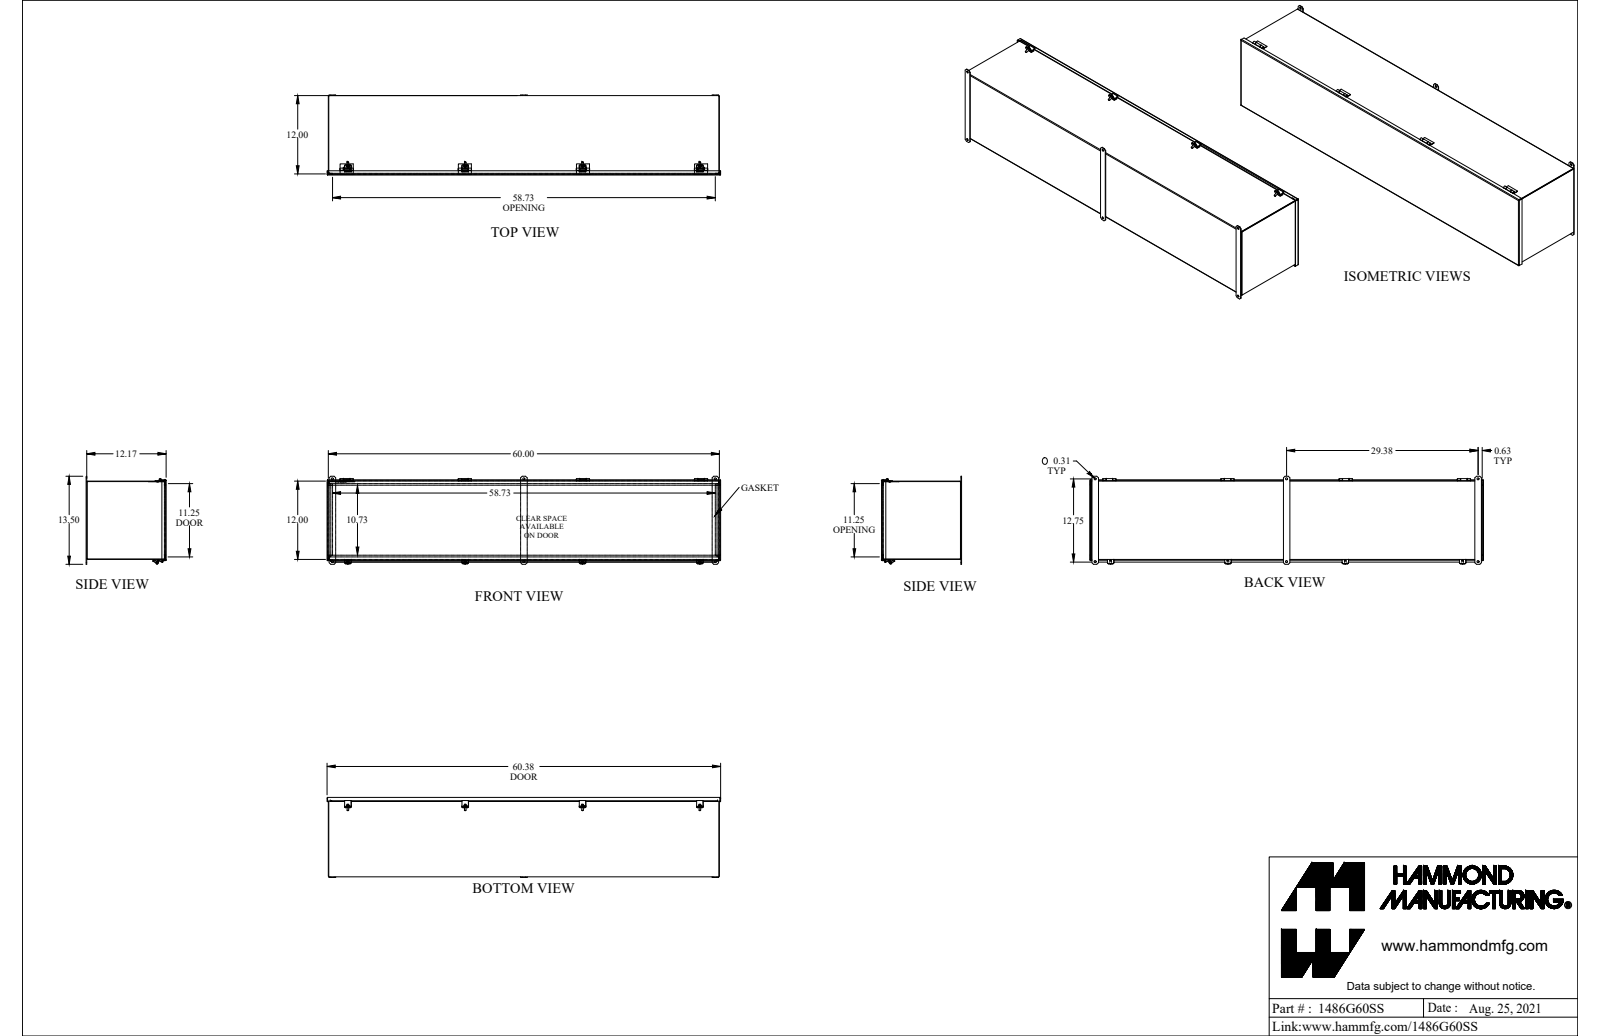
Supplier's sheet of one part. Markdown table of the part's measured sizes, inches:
| quantity | value |
| --- | --- |
| part name | 1486G60 |
| STEP written by | SolidWorks 2021 (AUTOMOTIVE_DESIGN) |
| units | inches |
| bodies | 16 solids, 624 faces (422 planar, 164 cylindrical, 38 other) |
| overall size | 60.375 × 13.5 × 12.267 |
| volume | 259.3 in³ |
| surface area | 6 963 in² |
| round holes (diameter × count) | 0.313 × 6, 0.213 × 4, 0.187 × 1 |
| round bosses / shafts (diameter × count) | 0.483 × 4, 0.25 × 4, 0.337 × 1, 0.18 × 1 |
| partial cylindrical surfaces (radius × count) | 0.188 × 16, 0.01 × 8, 0.03 × 8, 0.04 × 8, 0.11 × 8, 0.141 × 8, 0.036 × 5, 0.108 × 5 |
| main face-to-face distances | 0.07, 11.93, 0.07, 0.072, 12, 11.86, 12.102, 12.03, 12.172, 12.1 |
| hole center spacings | 12.688, 18, 29.375, 29.375, 31.998, 31.998, 36, 58.75 |
